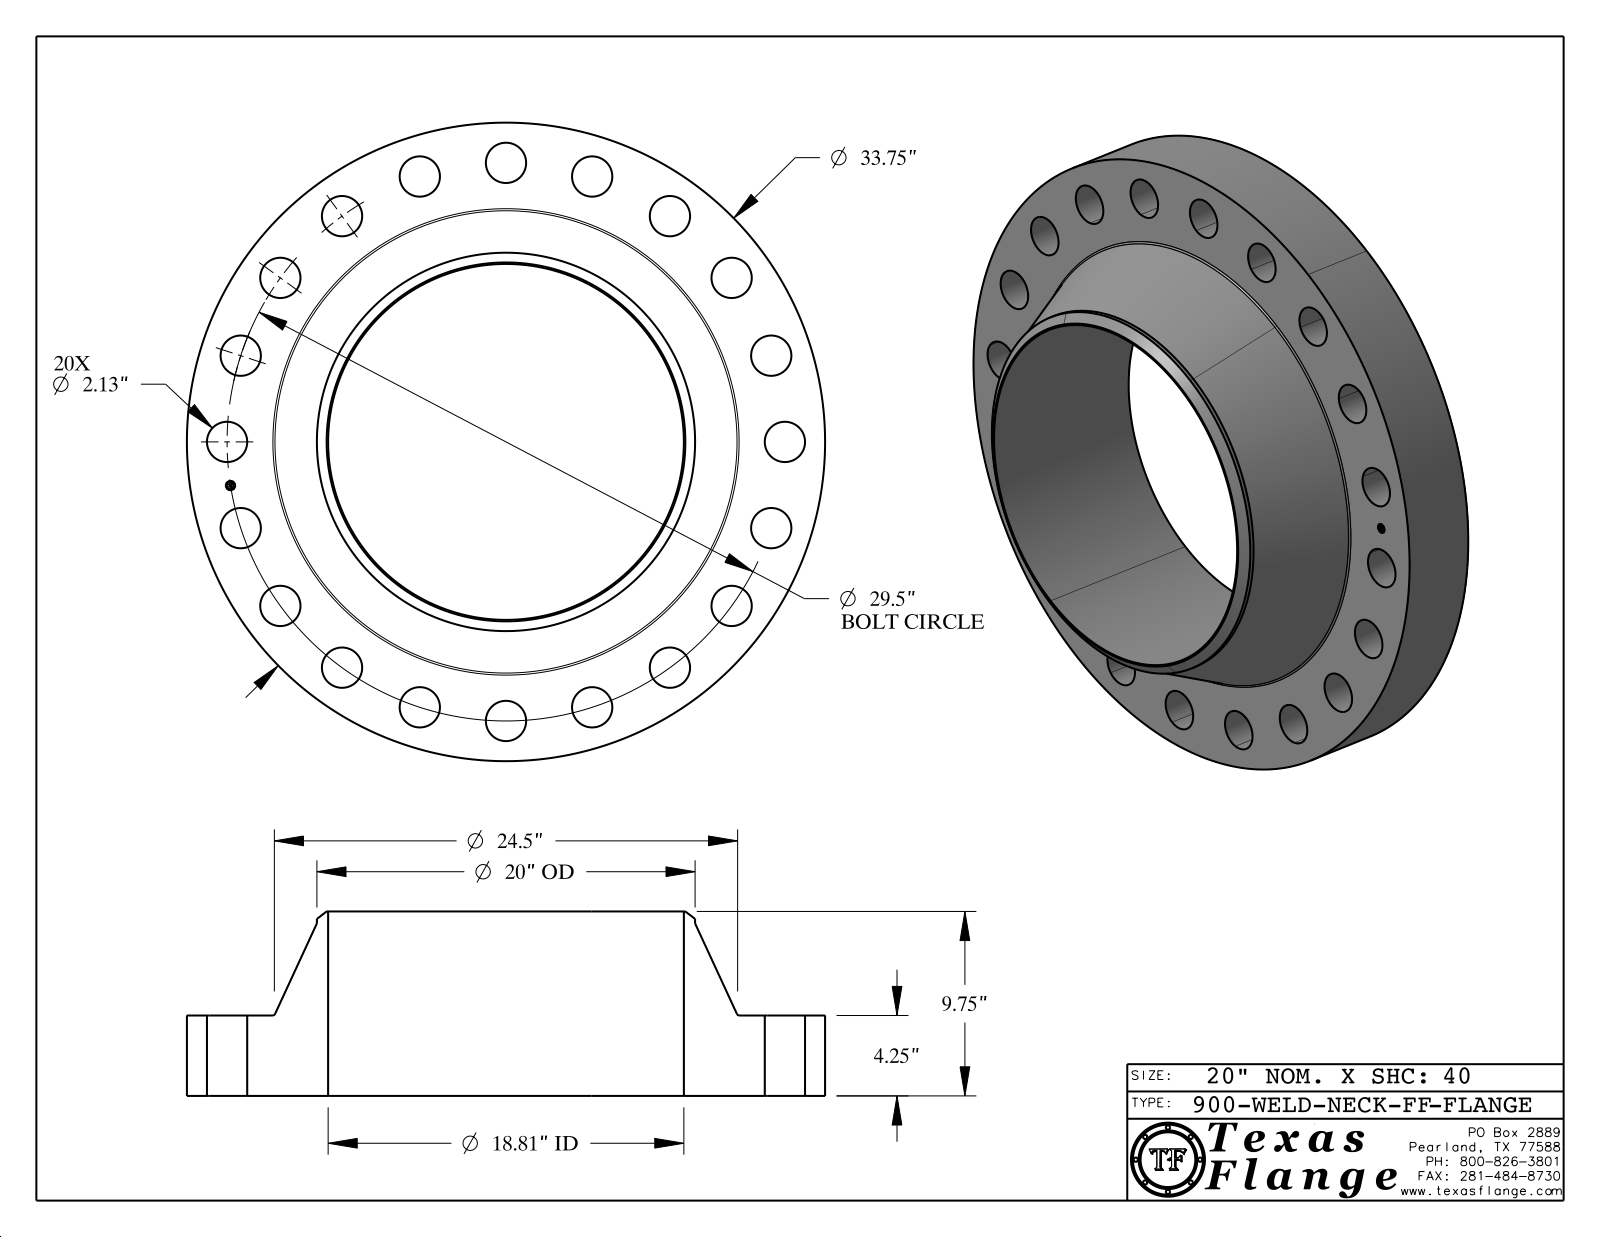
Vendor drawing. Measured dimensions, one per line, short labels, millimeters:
name: 900-WELD-NECK-FF
written by: CATIA V5 STEP AP214 (AUTOMOTIVE_DESIGN)
unit: mm
bodies: 1 solid, 440 faces (368 planar, 66 cylindrical, 6 other)
size: 857.3 × 857.3 × 247.7
volume: 47 210 000 mm³; area: 1 888 000 mm²
holes: 20× ⌀54.1, 1× ⌀12.6, 1× ⌀477.8
bosses: 8× ⌀0.8, 1× ⌀857.3, 1× ⌀508, 1× ⌀9.9
face distances: 108, 247.7, 139.7, 107.6, 0.4, 140.1, 3.8, 3.7, 0.7, 2.4
hole spacings: 374.7, 740.1, 117.2, 440.4, 529.8, 606.2, 667.6, 231.5
